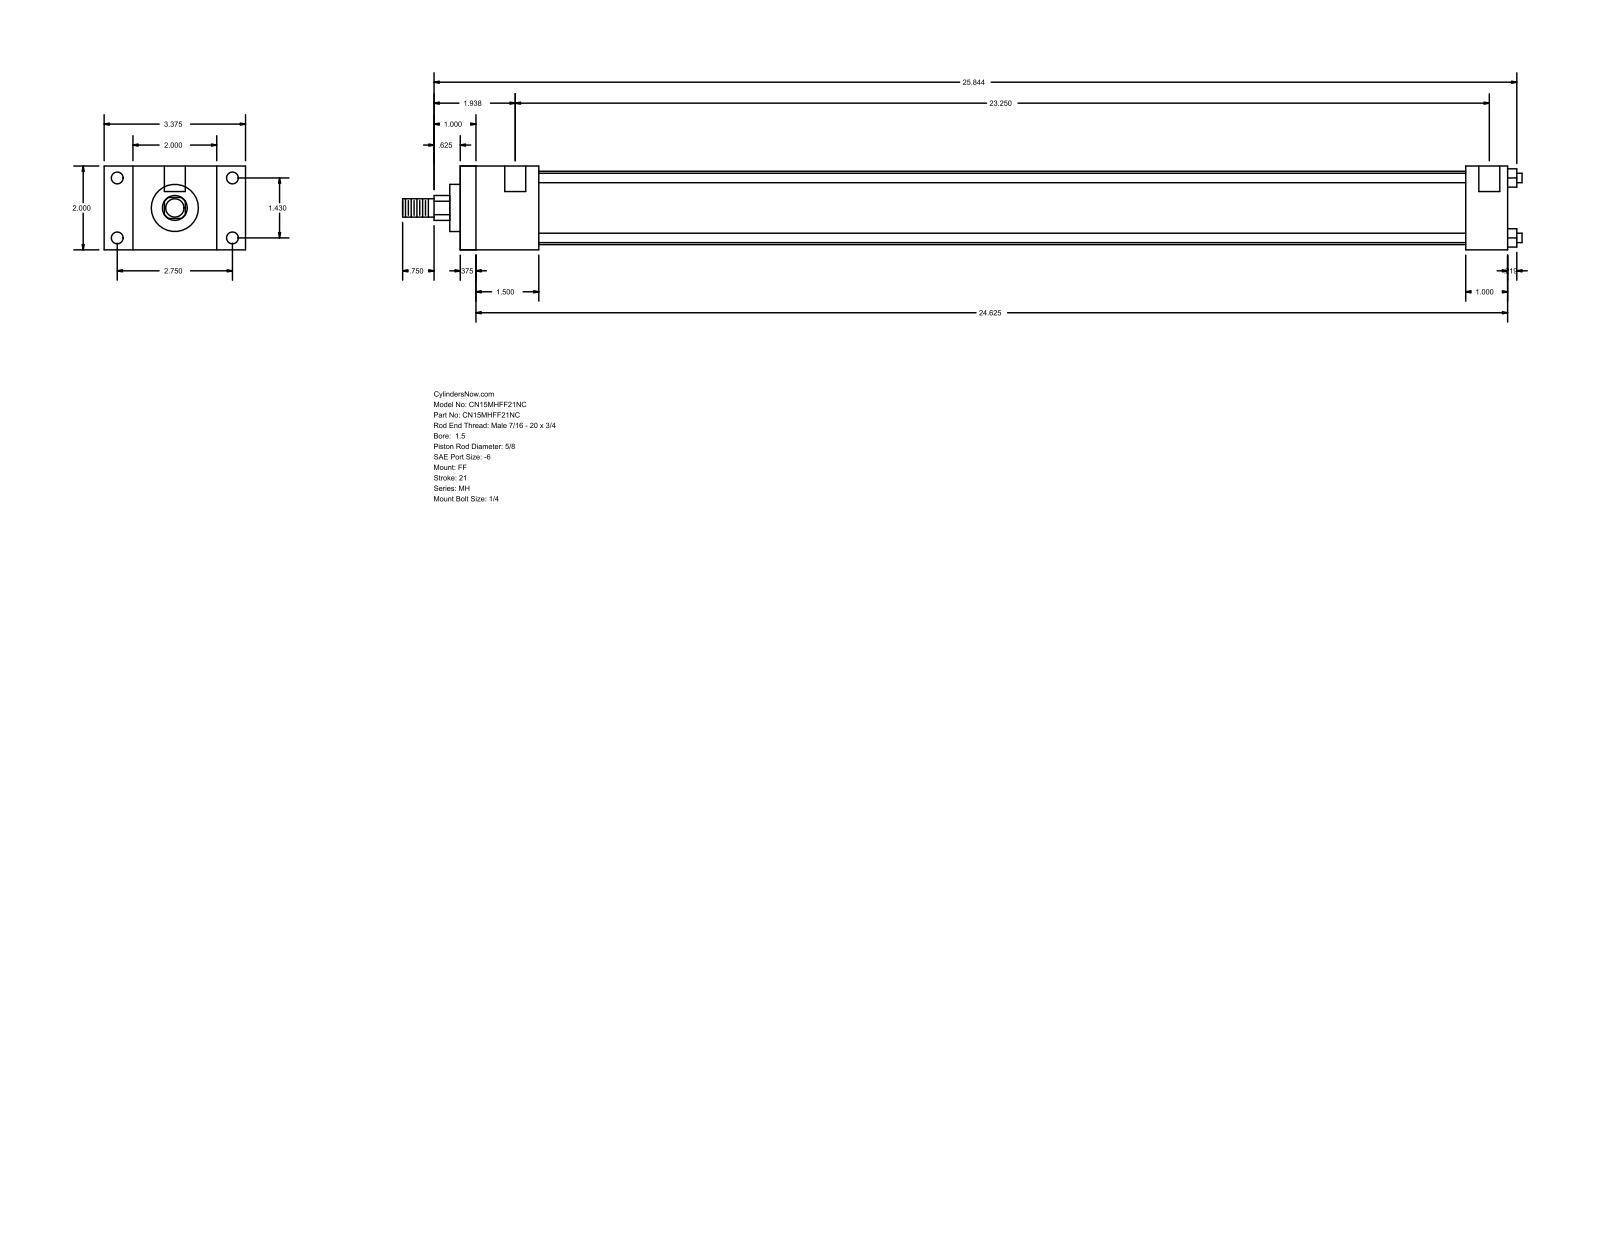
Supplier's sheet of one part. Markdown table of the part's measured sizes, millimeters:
| quantity | value |
| --- | --- |
| part name | MH_FF__0150_0.625 |
| STEP written by | GSSL Pune (CONFIG_CONTROL_DESIGN) |
| units | millimeters |
| bodies | 0 solids, 92 faces (64 planar, 28 cylindrical, 0 other) |
| overall size | 678.66 × 85.72 × 50.8 |
| round holes (diameter × count) | 5.56 × 4, 7.14 × 4, 12.7 × 2 |
| round bosses / shafts (diameter × count) | 5.71 × 4, 44.45 × 1, 28.57 × 1, 15.88 × 1, 11.11 × 1 |
| partial cylindrical surfaces (radius × count) | 7.54 × 1 |
| main face-to-face distances | 50.8, 635, 625.48, 9.52, 25.4, 17.46, 68.26, 47.62, 38.1, 587.38 |
| hole center spacings | 36.32, 69.84, 78.72, 593.72, 3.17, 590.55 |
